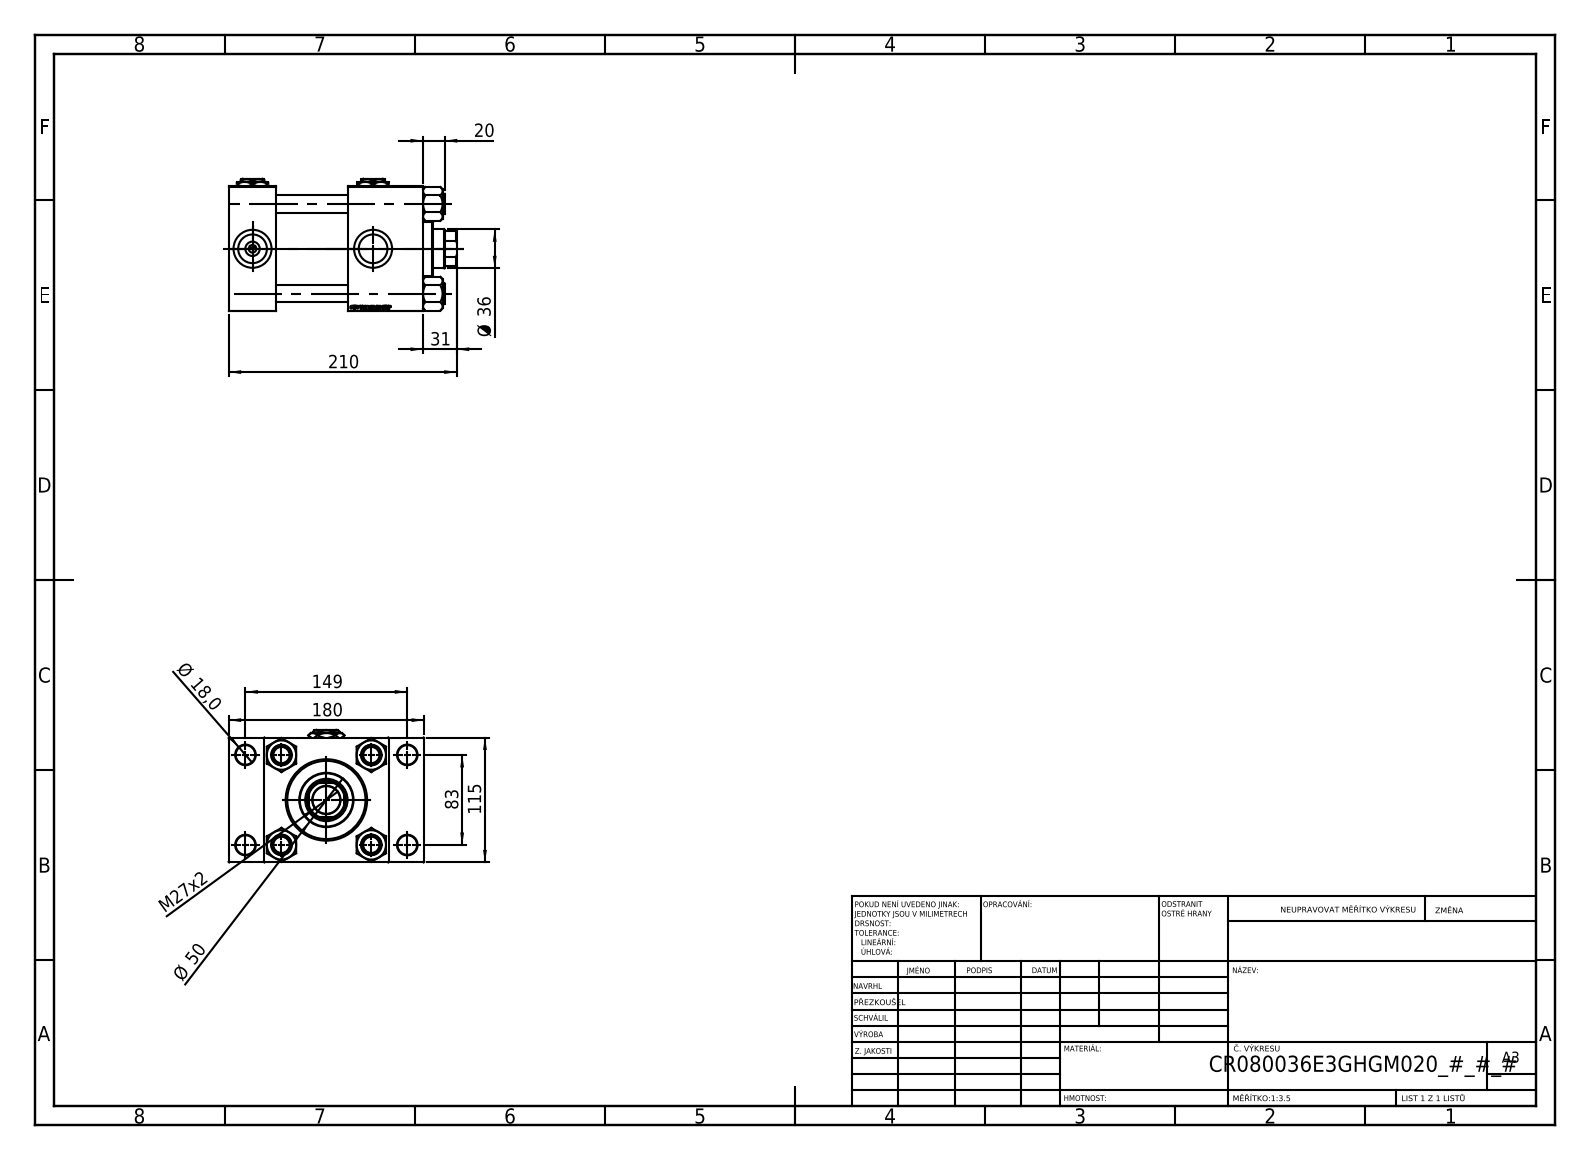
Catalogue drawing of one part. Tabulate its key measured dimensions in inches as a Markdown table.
| quantity | value |
| --- | --- |
| part name | V215CR_E_Body; V215_VC_A; V215CR_TYCINKA_E; V215CR_VCP_E (+2 more) |
| STEP written by | SolidWorks 2019 (CONFIG_CONTROL_DESIGN) |
| units | inches |
| bodies | 13 solids, 1284 faces (593 planar, 97 cylindrical, 594 other) |
| overall size | 8.268 × 7.087 × 4.803 |
| volume | 126.3 in³ |
| surface area | 491.8 in² |
| round holes (diameter × count) | 0.63 × 4, 0.709 × 4, 1.041 × 4, 1.378 × 4, 0.276 × 3, 1.004 × 1, 1.417 × 1, 1.535 × 1, 2.402 × 1, 2.835 × 1, 3.15 × 1 |
| round bosses / shafts (diameter × count) | 0.748 × 4, 3.386 × 1, 1.969 × 1 |
| partial cylindrical surfaces (radius × count) | 0.689 × 1 |
| main face-to-face distances | 4.528, 1.732, 7.047, 5.315, 1.28, 5.807, 4.331, 2.717, 2.598, 3.504 |
| hole center spacings | 1.305, 2.302, 3.256, 3.357, 3.513, 4.561, 5.607, 3.268 |
